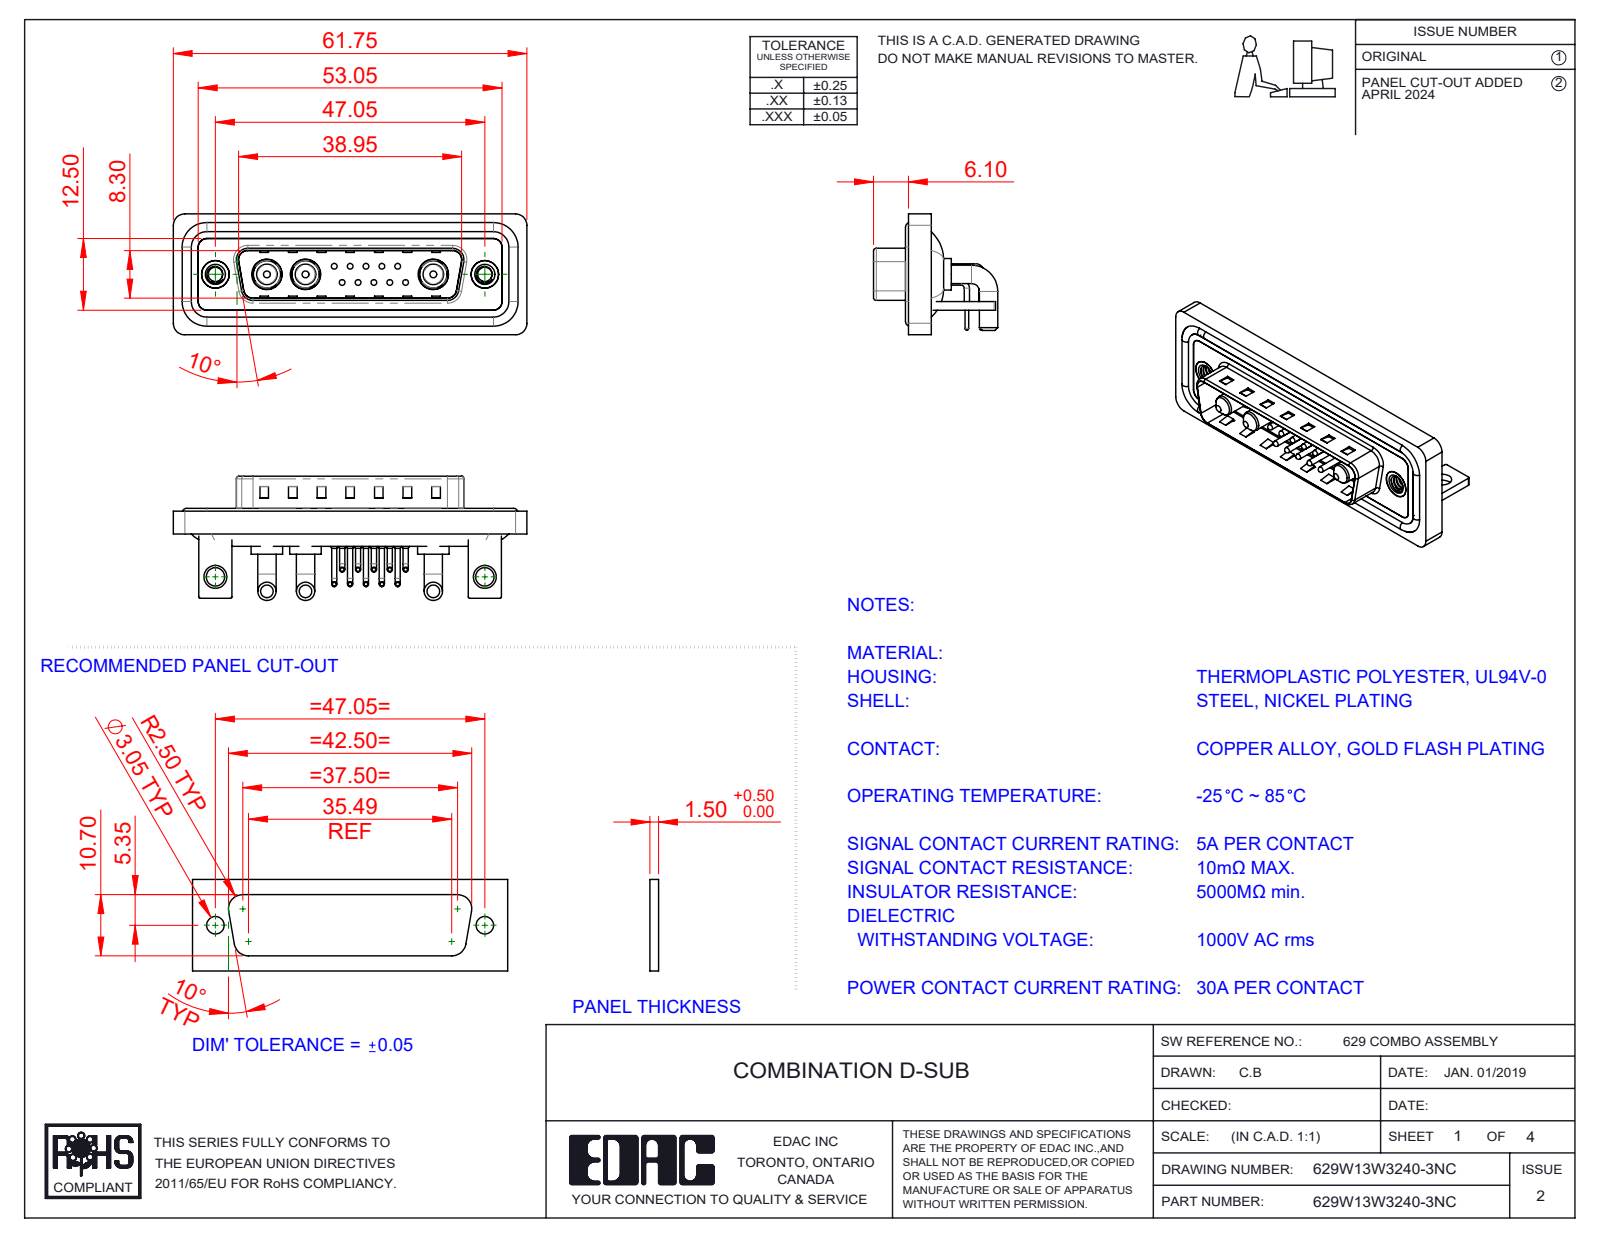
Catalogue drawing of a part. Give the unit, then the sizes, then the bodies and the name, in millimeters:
Units: millimetres
Overall size (bounding box): 61.75 × 21.7 × 21.1
Round holes (diameter × count): ⌀0.75 ×10, ⌀1.6 ×10, ⌀2 ×10, ⌀4.85 ×3, ⌀5.3 ×3, ⌀2.5 ×2, ⌀3.2 ×2, ⌀4 ×2, ⌀4.8 ×2, ⌀5 ×2
Round bosses / shafts (diameter × count): ⌀0.9 ×20, ⌀1.5 ×10, ⌀1 ×10, ⌀0.65 ×10, ⌀3.2 ×6, ⌀1.6 ×4, ⌀5.5 ×3, ⌀5.2 ×3
Partial cylindrical surfaces — rounded edges, fillets, slot ends (radius × count): R2 ×19, R1.5 ×18, R0.25 ×16, R1.01 ×10, R0.5 ×9, R1.6 ×8, R0.6 ×4, R0.65 ×4
Main face-to-face distances: 0.4, 0.8, 1.5, 2.9, 2.1, 1.1, 4.1, 1.6, 3.7, 4.5
Hole centre spacings: 3.16, 2.77, 5.04, 5.54, 7.49, 5.03, 8.31, 10.11
Volume: 7 966 mm³ · Surface area: 13 140 mm²
Bodies: 25 solids, 1750 faces (899 planar, 629 cylindrical, 222 other)
Part name (STEP PRODUCT): 629Combo Contact Row 2; 629Combo Shell Front_25 Contacts; 629Combo Shell Rear_25 Contacts; 629Combo Threaded Rivet_B (+6 more)
STEP written by: SolidWorks 2023 (CONFIG_CONTROL_DESIGN)
